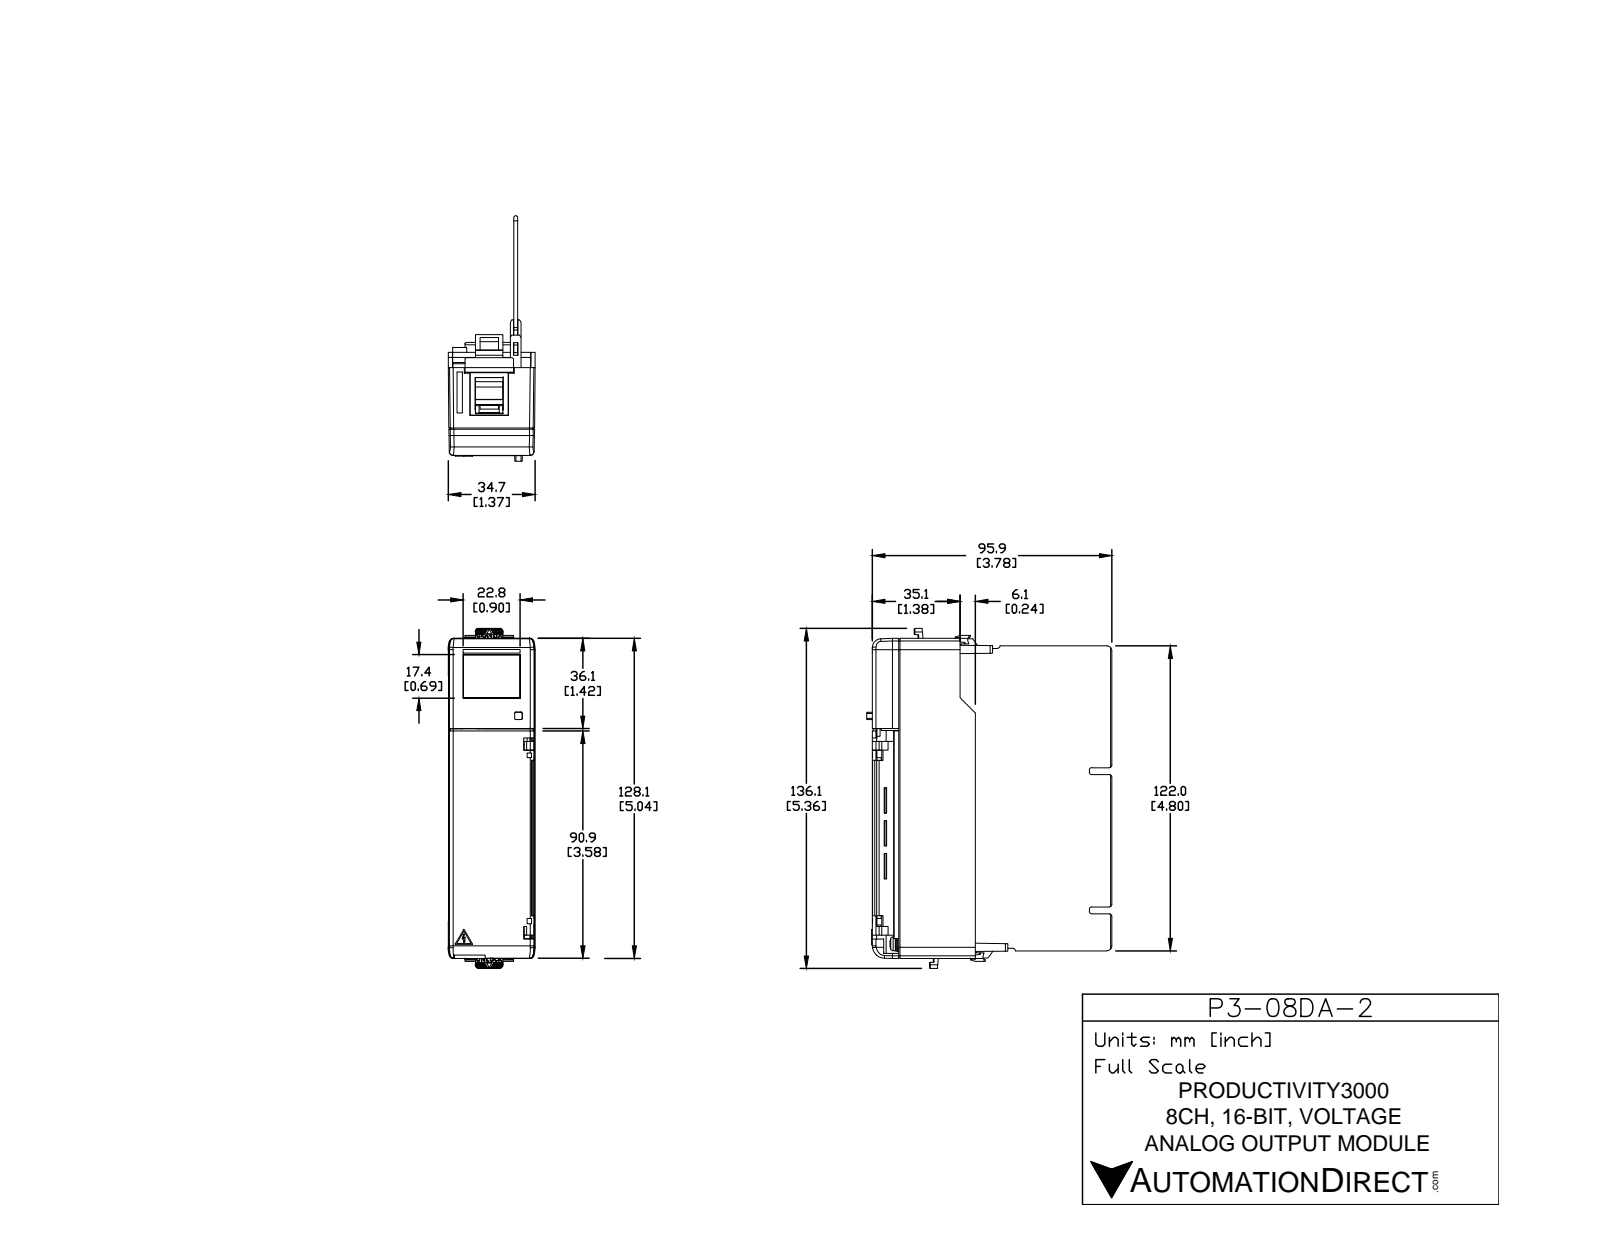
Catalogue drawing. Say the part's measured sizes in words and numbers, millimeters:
The part is named "P3-08DA-2". Its 3-D file was written by "SolidWorks 2009 (CONFIG_CONTROL_DESIGN)". It is 1 solid with 3823 faces: 2833 planar, 744 cylindrical and 246 other. Overall it measures 136.08 by 98.18 by 34.8 millimeters. Its volume is 101 360 cubic millimeters and its surface area 75 361 square millimeters. Round holes: 22 of diameter 3.2, 2 of diameter 5, 1 of diameter 1.8. Round bosses or shafts: 22 of diameter 5.5, 22 of diameter 3, 20 of diameter 2.4, 2 of diameter 5.6, 2 of diameter 2.2, 2 of diameter 2, 1 of diameter 1.5. Partial cylindrical surfaces (rounded edges, fillets, slot ends): 95 of radius 0.5, 33 of radius 1, 29 of radius 0.3, 22 of radius 1.67, 13 of radius 1.5, 6 of radius 2, 5 of radius 0.2, 4 of radius 0.1. The main face-to-face distances are 1.6, 1.7, 28.23, 26.53, 32.56, 22.2, 2.2, 7.9, 6.8, 5.32. The hole center spacings are 8.68, 7.62, 13.84, 15.24, 20.59, 22.86, 27.79, 30.48.
